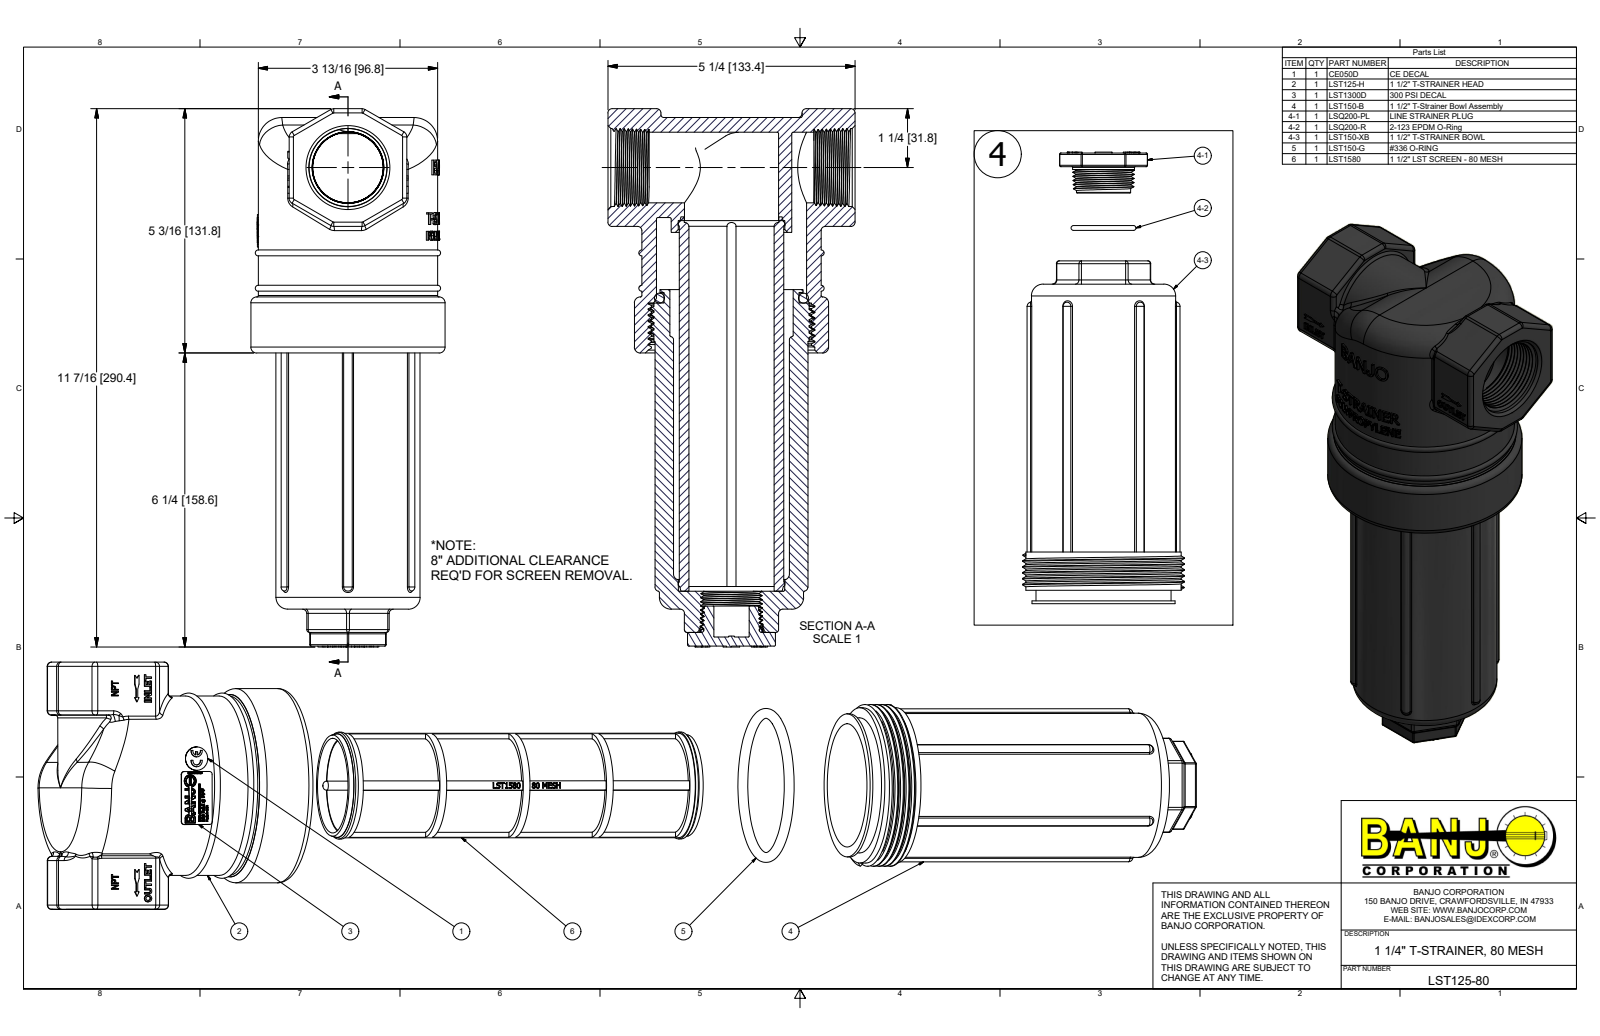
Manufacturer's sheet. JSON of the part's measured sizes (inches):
{"part_name": "LST125-80; CE050D; LST125-H; LST1300D (+6 more)", "step_written_by": "Autodesk Inventor 2018 (AUTOMOTIVE_DESIGN)", "units": "inches", "bodies": {"solids": 8, "faces": 3130, "planar": 1682, "cylindrical": 298, "other": 1150}, "overall_size": [48.286, 11.433, 4.125], "volume_in3": 50.28, "surface_area_in2": 752.8, "round_holes": [[0.181, 1], [0.257, 1], [0.75, 1], [1.5, 1], [1.81, 1], [1.97, 1], [2, 1], [2.26, 1], [2.265, 1], [2.62, 1], [3.19, 1], [3.403, 1]], "round_bosses_or_shafts": [[4.125, 1], [3.81, 1], [3.435, 1], [3.3, 1], [3.063, 1], [3.04, 1], [2.87, 1], [2.563, 1]], "partial_cylinders_radius": [[0.03, 44], [0.09, 34], [0.06, 16], [0.125, 10], [0.078, 6], [0.094, 6], [0.1, 4], [0.026, 2]], "face_to_face_distances": [2.5, 10.06, 6.12, 3.94, 0.92, 1.24, 9.748, 3.628, 0.313, 5.25]}
